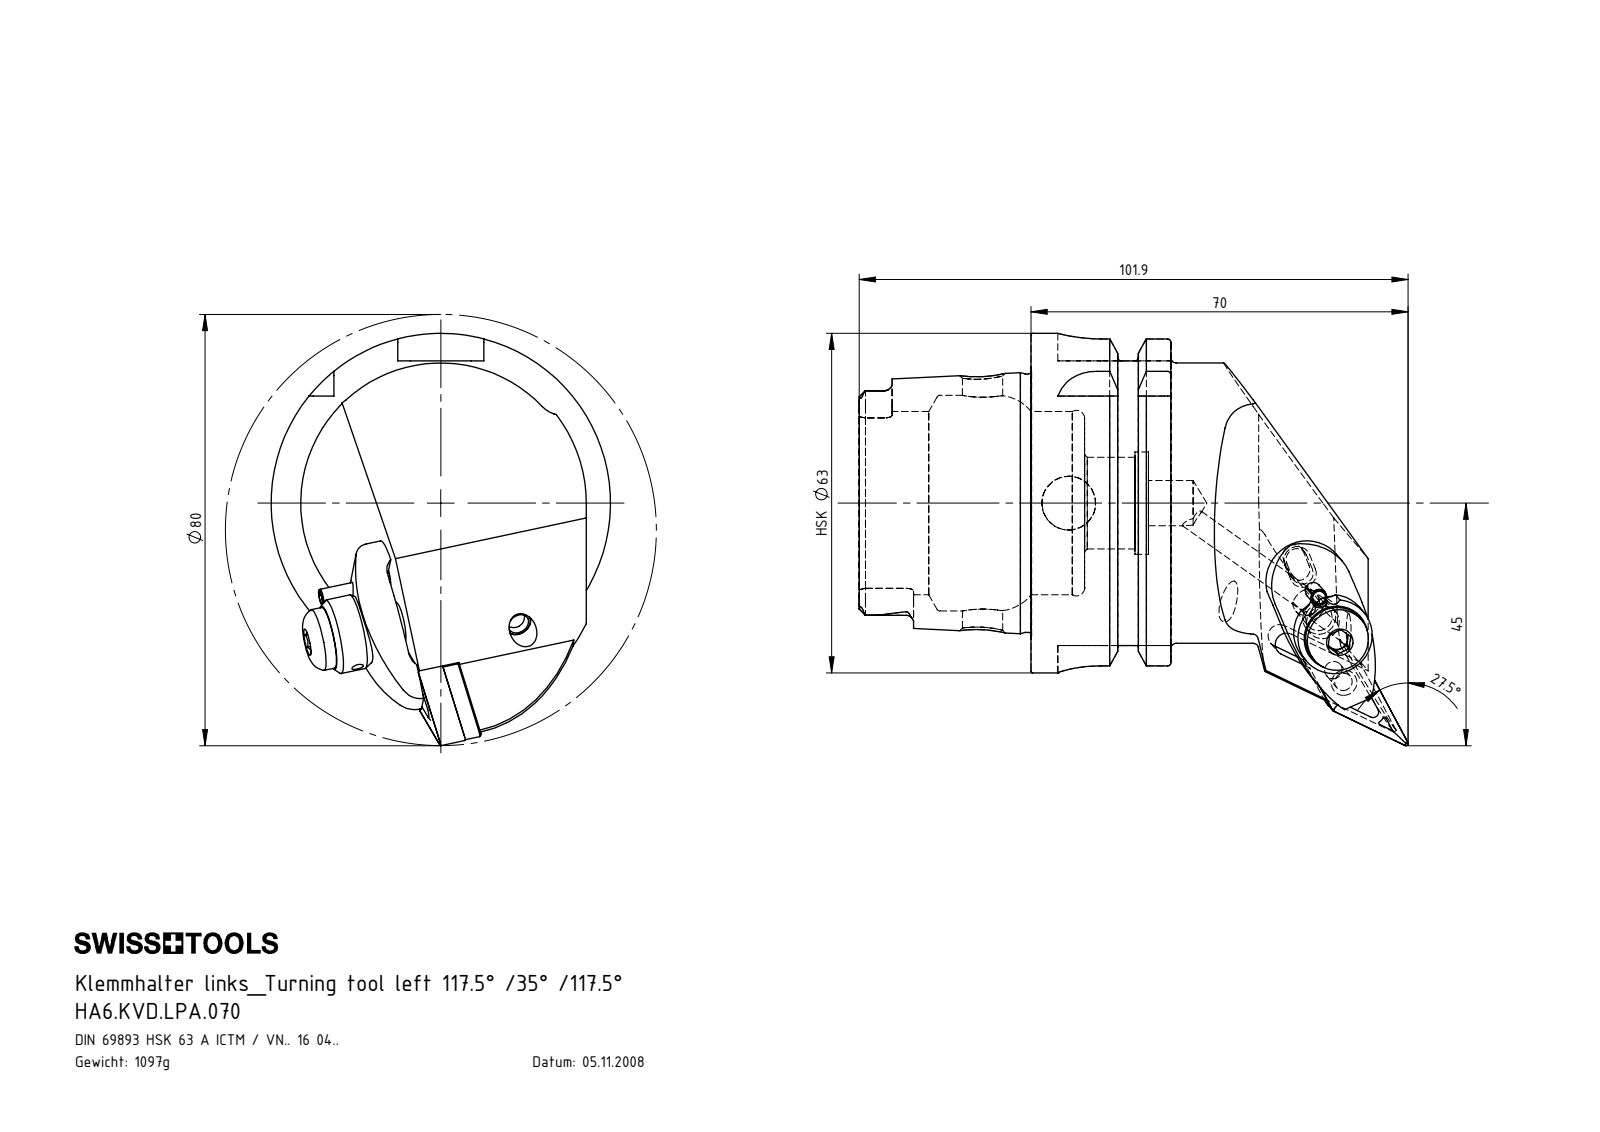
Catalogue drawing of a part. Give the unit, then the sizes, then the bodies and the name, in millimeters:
Units: millimetres
Overall size (bounding box): 101.9 × 76.5 × 63
Round holes (diameter × count): ⌀2 ×3, ⌀5 ×2, ⌀7 ×2, ⌀2.4 ×1, ⌀3 ×1, ⌀3.3 ×1, ⌀3.8 ×1, ⌀4 ×1, ⌀4.2 ×1, ⌀4.95 ×1, ⌀6.2 ×1, ⌀6.9 ×1
Round bosses / shafts (diameter × count): ⌀4 ×2, ⌀3 ×2, ⌀63 ×1, ⌀54.95 ×1, ⌀52 ×1, ⌀47.94 ×1, ⌀14 ×1, ⌀11.5 ×1
Partial cylindrical surfaces — rounded edges, fillets, slot ends (radius × count): R0.34 ×6, R0.59 ×6, R1.4 ×6, R0.4 ×4, R8 ×4, R1.5 ×3, R40 ×3, R0.5 ×2
Main face-to-face distances: 25.95, 16, 9.95, 31.9, 41.85, 57.85, 52.8, 21.8, 4.44, 11.85
Hole centre spacings: 14.3, 8.19, 14.31, 8.21, 22.49, 22.5, 8.2, 14.29
Volume: 138 593 mm³ · Surface area: 33 812 mm²
Bodies: 11 solids, 469 faces (125 planar, 153 cylindrical, 191 other)
Part name (STEP PRODUCT): WCC-ER3.102.024_C; ISO 13337 - 3 x 12_PreviewCfg; WVD-ER2.101.003_A; KVT_MB_600_050 (+7 more)
STEP written by: SolidWorks 2017 (AUTOMOTIVE_DESIGN)
